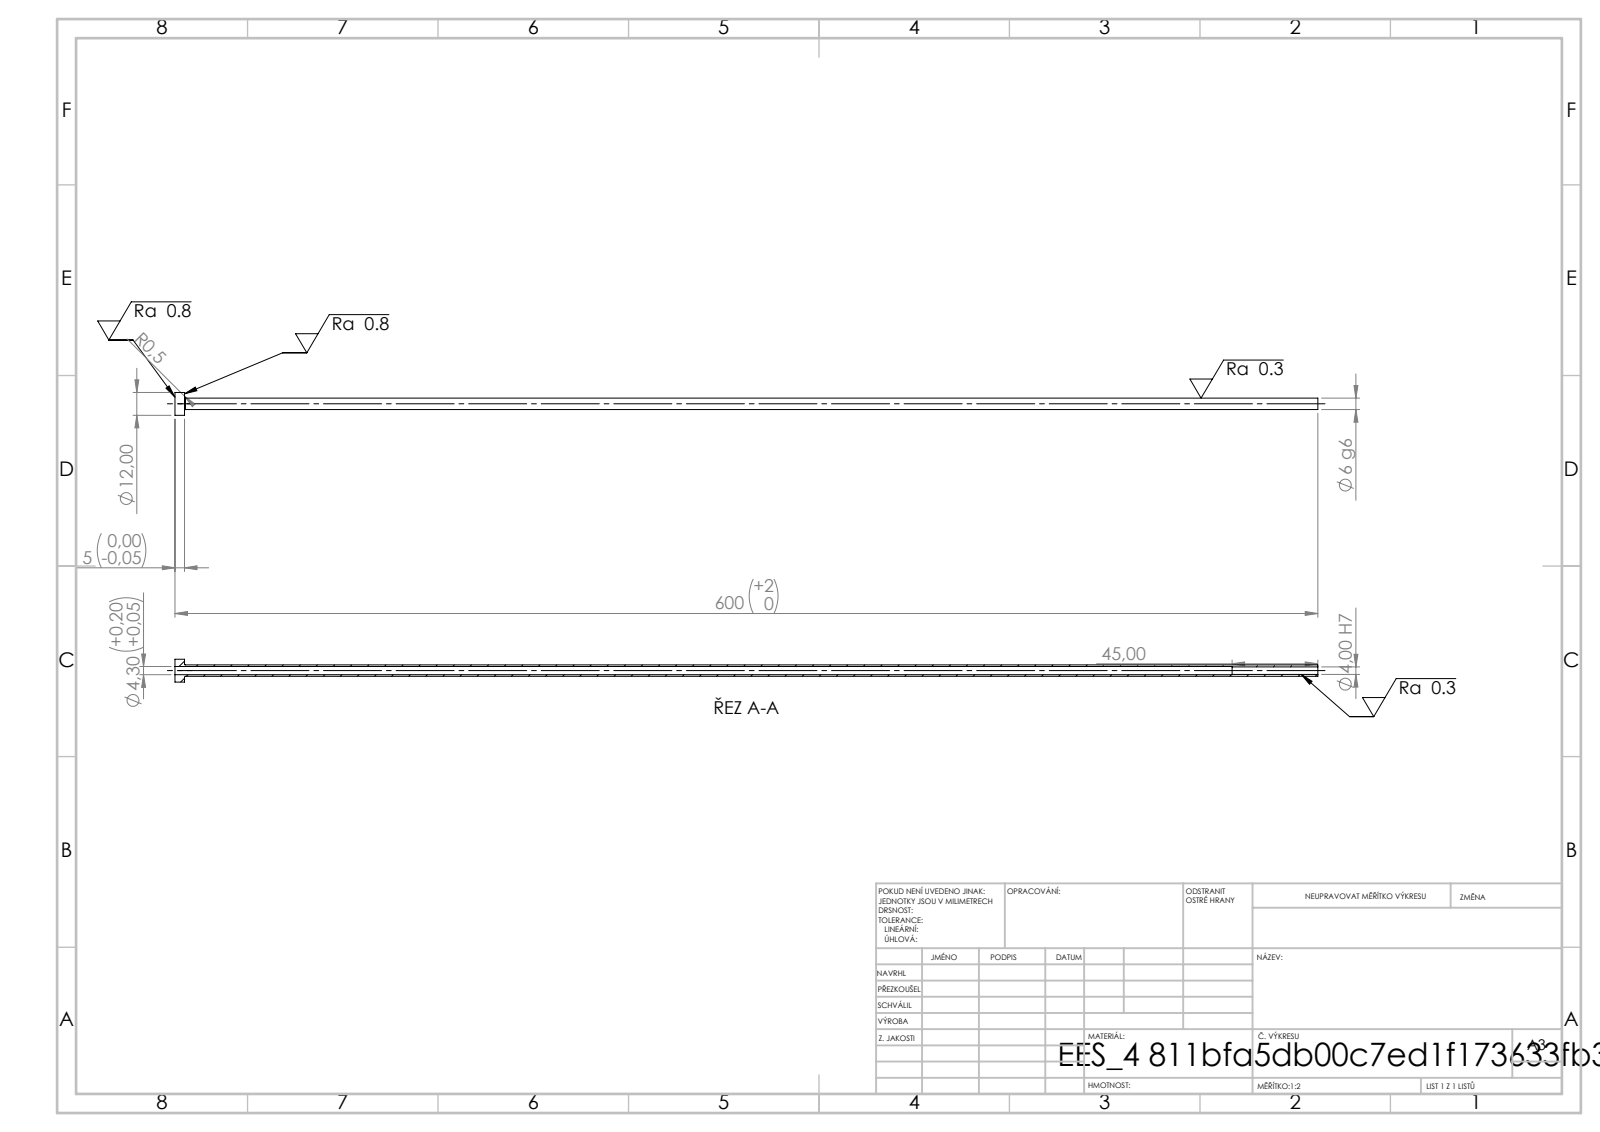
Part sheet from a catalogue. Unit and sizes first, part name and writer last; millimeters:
Units: millimetres
Overall size (bounding box): 600 × 12 × 12
Round holes (diameter × count): ⌀4 ×1, ⌀4.3 ×1
Round bosses / shafts (diameter × count): ⌀12 ×1, ⌀6 ×1
Main face-to-face distances: 5, 600, 595, 555, 550, 45
Volume: 8 765 mm³ · Surface area: 19 664 mm²
Bodies: 1 solid, 14 faces (4 planar, 8 cylindrical, 2 other)
STEP written by: SolidWorks 2019 (CONFIG_CONTROL_DESIGN)
